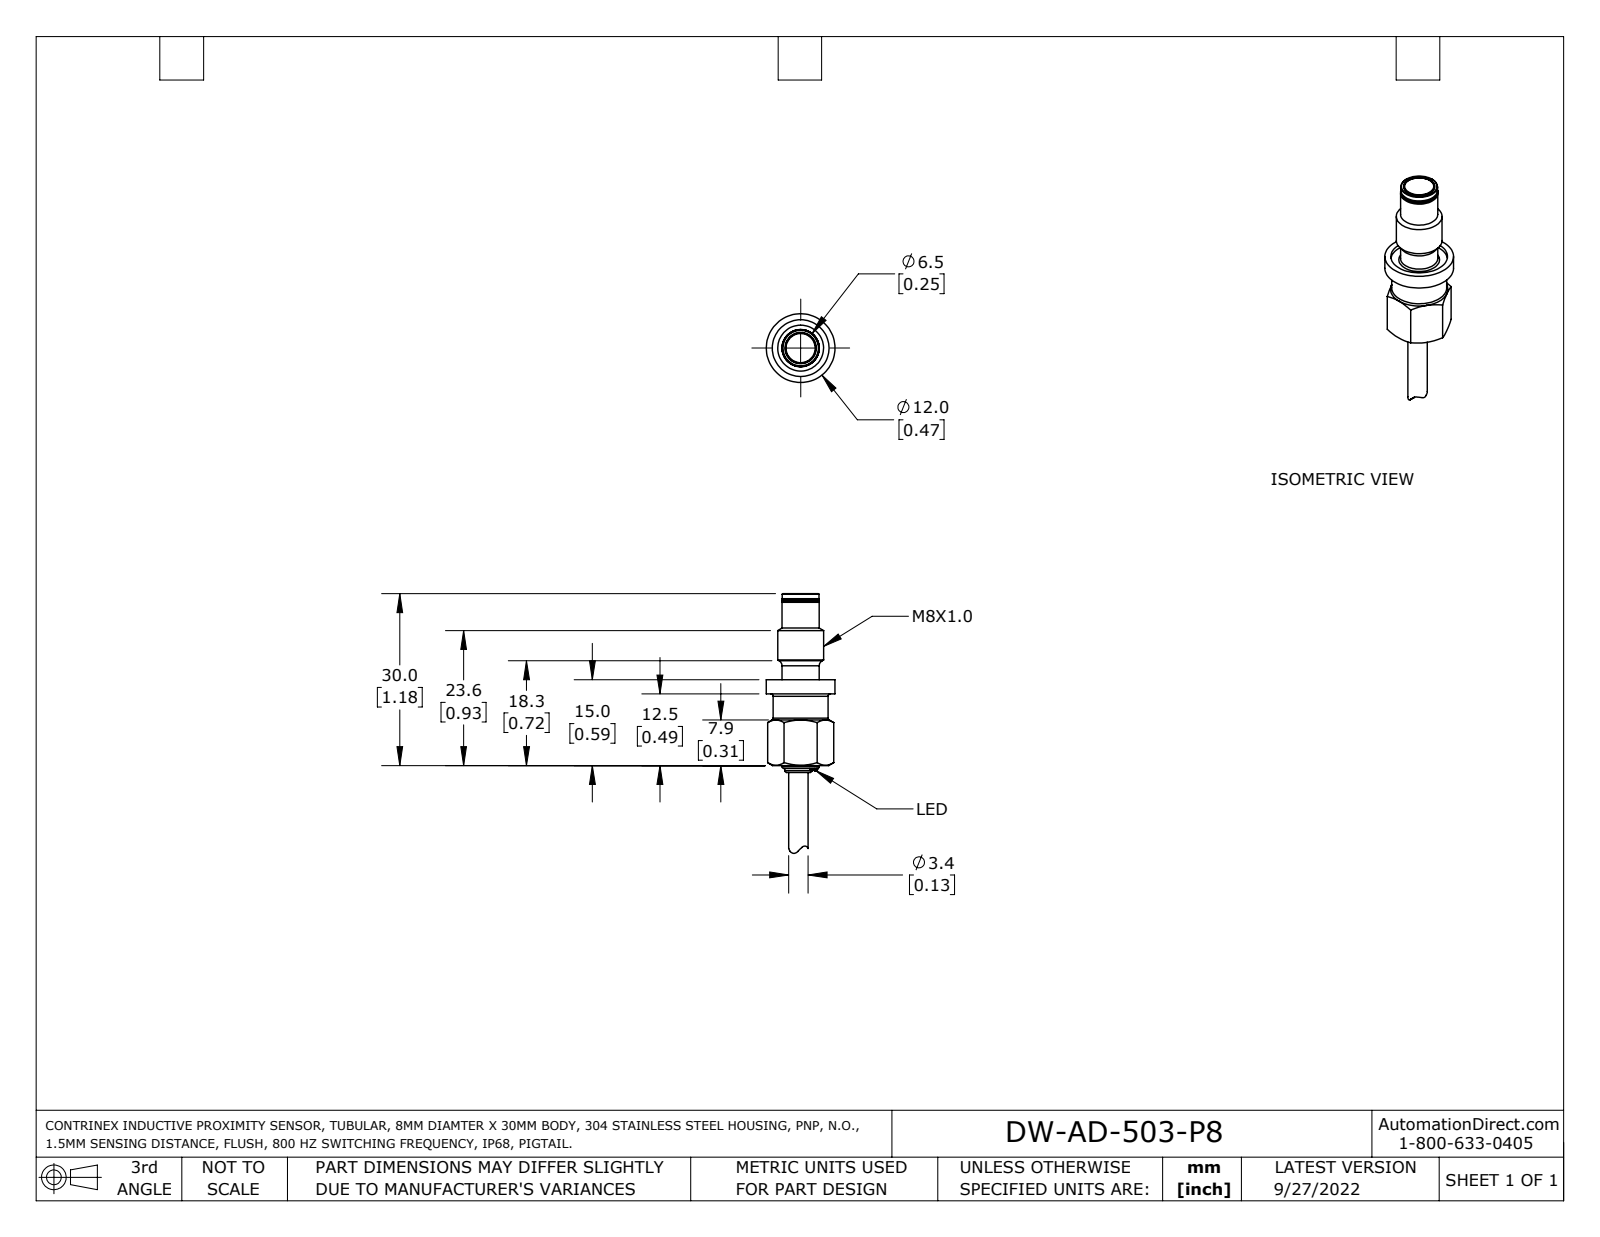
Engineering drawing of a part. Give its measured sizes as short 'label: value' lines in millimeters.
name: DW-AD-503-P8
written by: SolidWorks 2021 (AUTOMOTIVE_DESIGN)
unit: mm
bodies: 1 solid, 88 faces (41 planar, 21 cylindrical, 26 other)
size: 45.3 × 12 × 12
volume: 2 030 mm³; area: 1 286 mm²
holes: 1× ⌀3.5, 1× ⌀9.9
bosses: 1× ⌀12, 1× ⌀9.6, 1× ⌀8, 1× ⌀6.5, 1× ⌀6.4, 1× ⌀4.7, 1× ⌀3.4
rounds: 2× R0.3, 1× R0.6, 1× R0.8, 1× R2.9, 1× R3.4, 1× R5.1, 1× R6.8
face distances: 10, 15, 0.7, 14.3, 15.7, 30, 2.5, 17.5, 1.8, 12.5
hole spacings: 0.4
